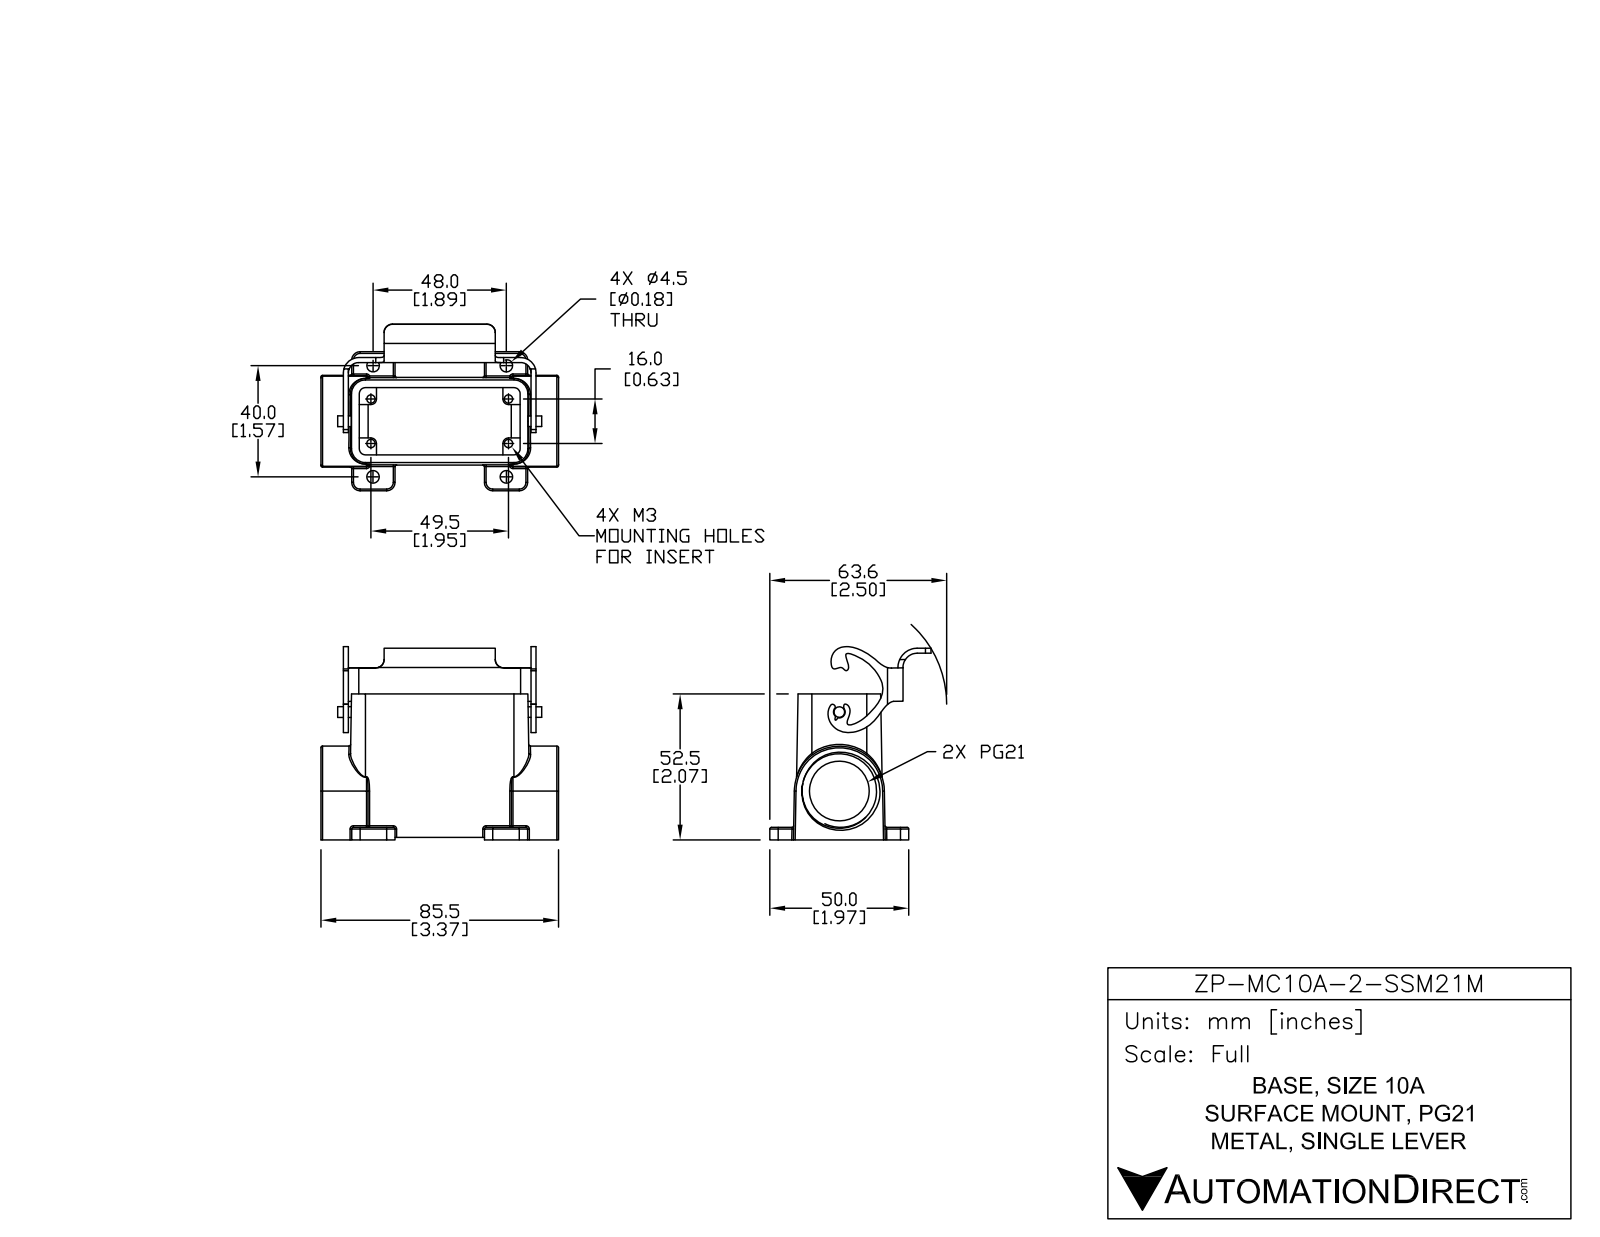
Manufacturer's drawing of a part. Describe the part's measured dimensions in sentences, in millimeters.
The part is named "ZP-MC10A-2-SSM21M". Its 3-D file was written by "SolidWorks 2014 (AUTOMOTIVE_DESIGN)". It is 2 solids with 272 faces: 91 planar, 111 cylindrical and 70 other. Overall it measures 85.5 by 69.46 by 59.93 millimeters. Its volume is 47 218 cubic millimeters and its surface area 33 873 square millimeters. Round holes: 4 of diameter 3, 4 of diameter 4.5, 1 of diameter 21.5, 1 of diameter 26.8. Round bosses or shafts: 1 of diameter 3.9, 1 of diameter 3.8. Partial cylindrical surfaces (rounded edges, fillets, slot ends): 32 of radius 0.6, 12 of radius 3, 4 of radius 2, 2 of radius 3.75, 2 of radius 5.55, 1 of radius 2.1, 1 of radius 5.1, 1 of radius 6.9. The main face-to-face distances are 2.77, 2.78, 4.44, 3.52, 1.8, 0.92, 20, 65.5, 51.5, 0.75. The hole center spacings are 28.01, 12.02, 12.03, 16, 40, 49.5, 50.08, 50.21.
